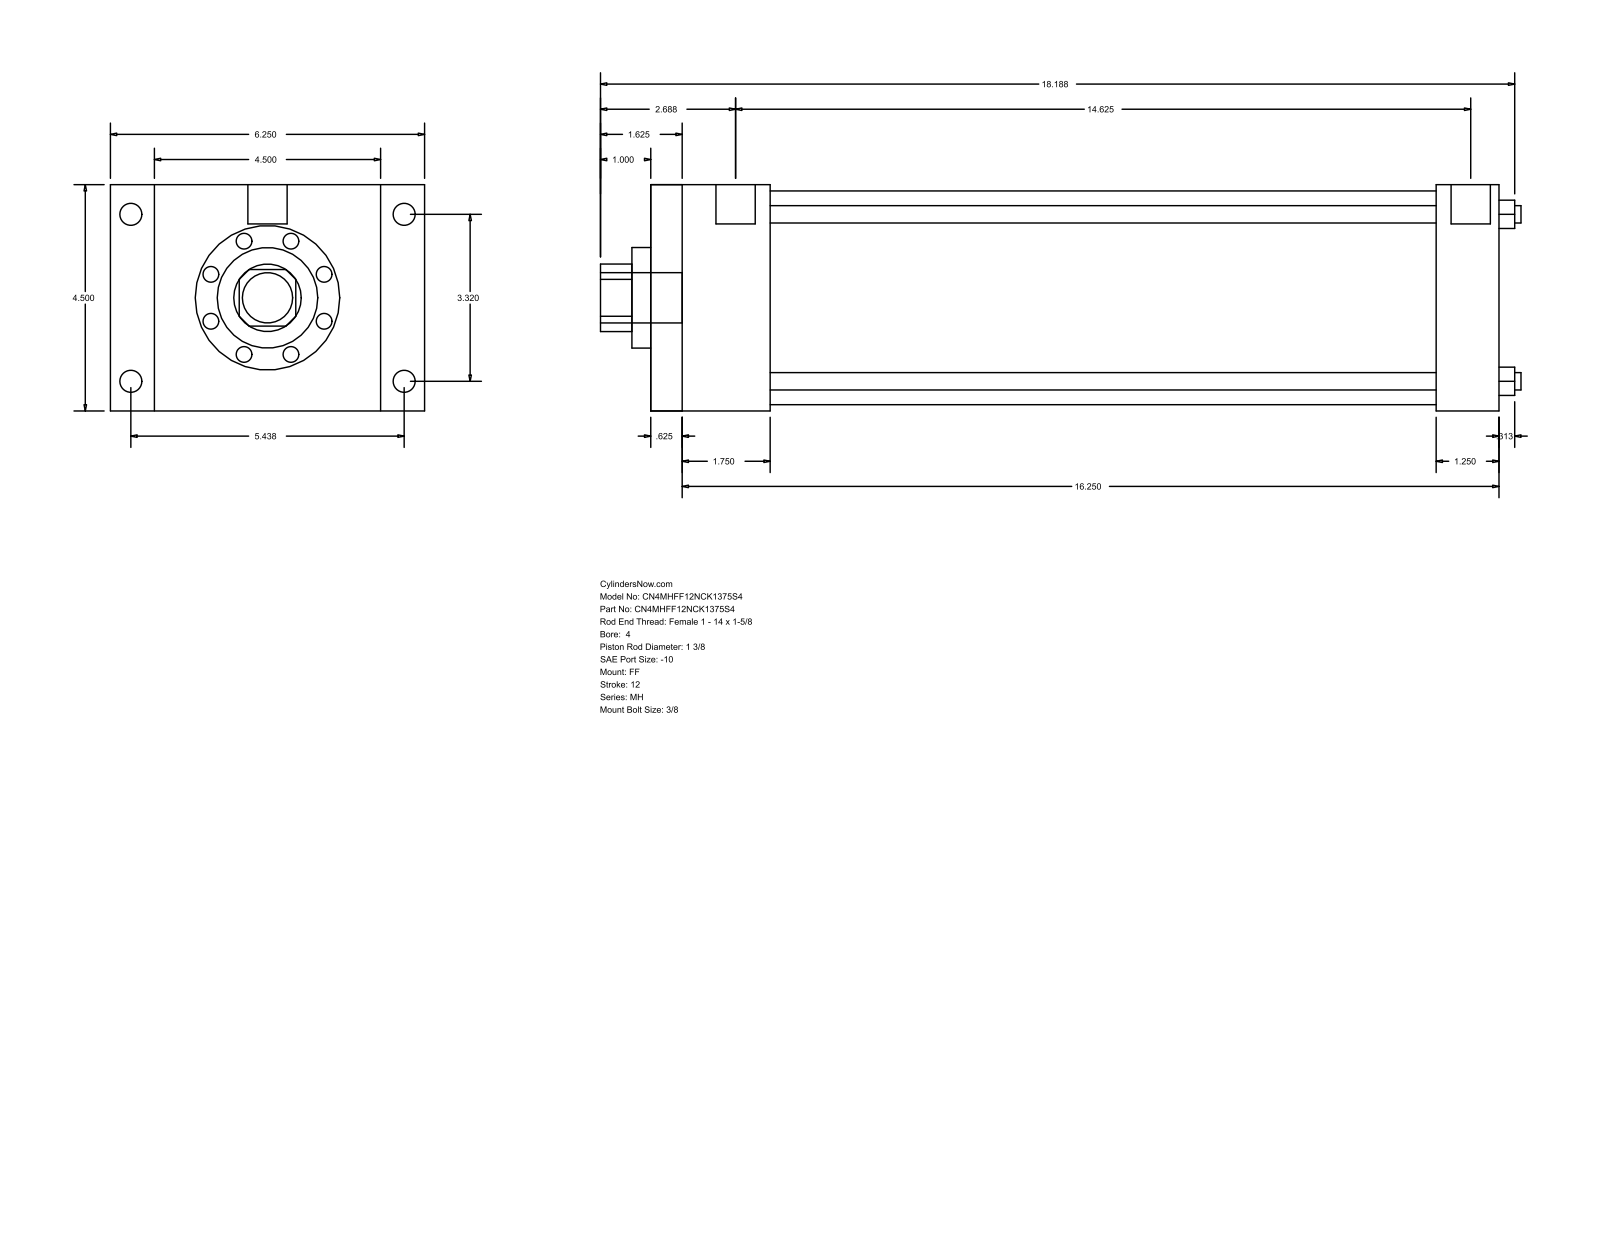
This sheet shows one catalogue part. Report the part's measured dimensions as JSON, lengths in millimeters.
{"part_name": "MH_FF__0400_1.375", "step_written_by": "GSSL Pune (CONFIG_CONTROL_DESIGN)", "units": "millimeters", "bodies": {"solids": 0, "faces": 92, "planar": 64, "cylindrical": 28, "other": 0}, "overall_size": [465.14, 158.75, 114.3], "round_holes": [[8.76, 4], [34.92, 1], [50.8, 1], [107.95, 1]], "round_bosses_or_shafts": [[11.13, 4], [8.73, 4], [19.84, 2], [25.4, 1]], "partial_cylinders_radius": [[17.06, 1]], "face_to_face_distances": [114.3, 428.62, 15.87, 412.75, 60.32, 44.45, 368.3, 396.87, 381, 336.55], "hole_center_spacings": [59.62, 84.32, 119.25]}
